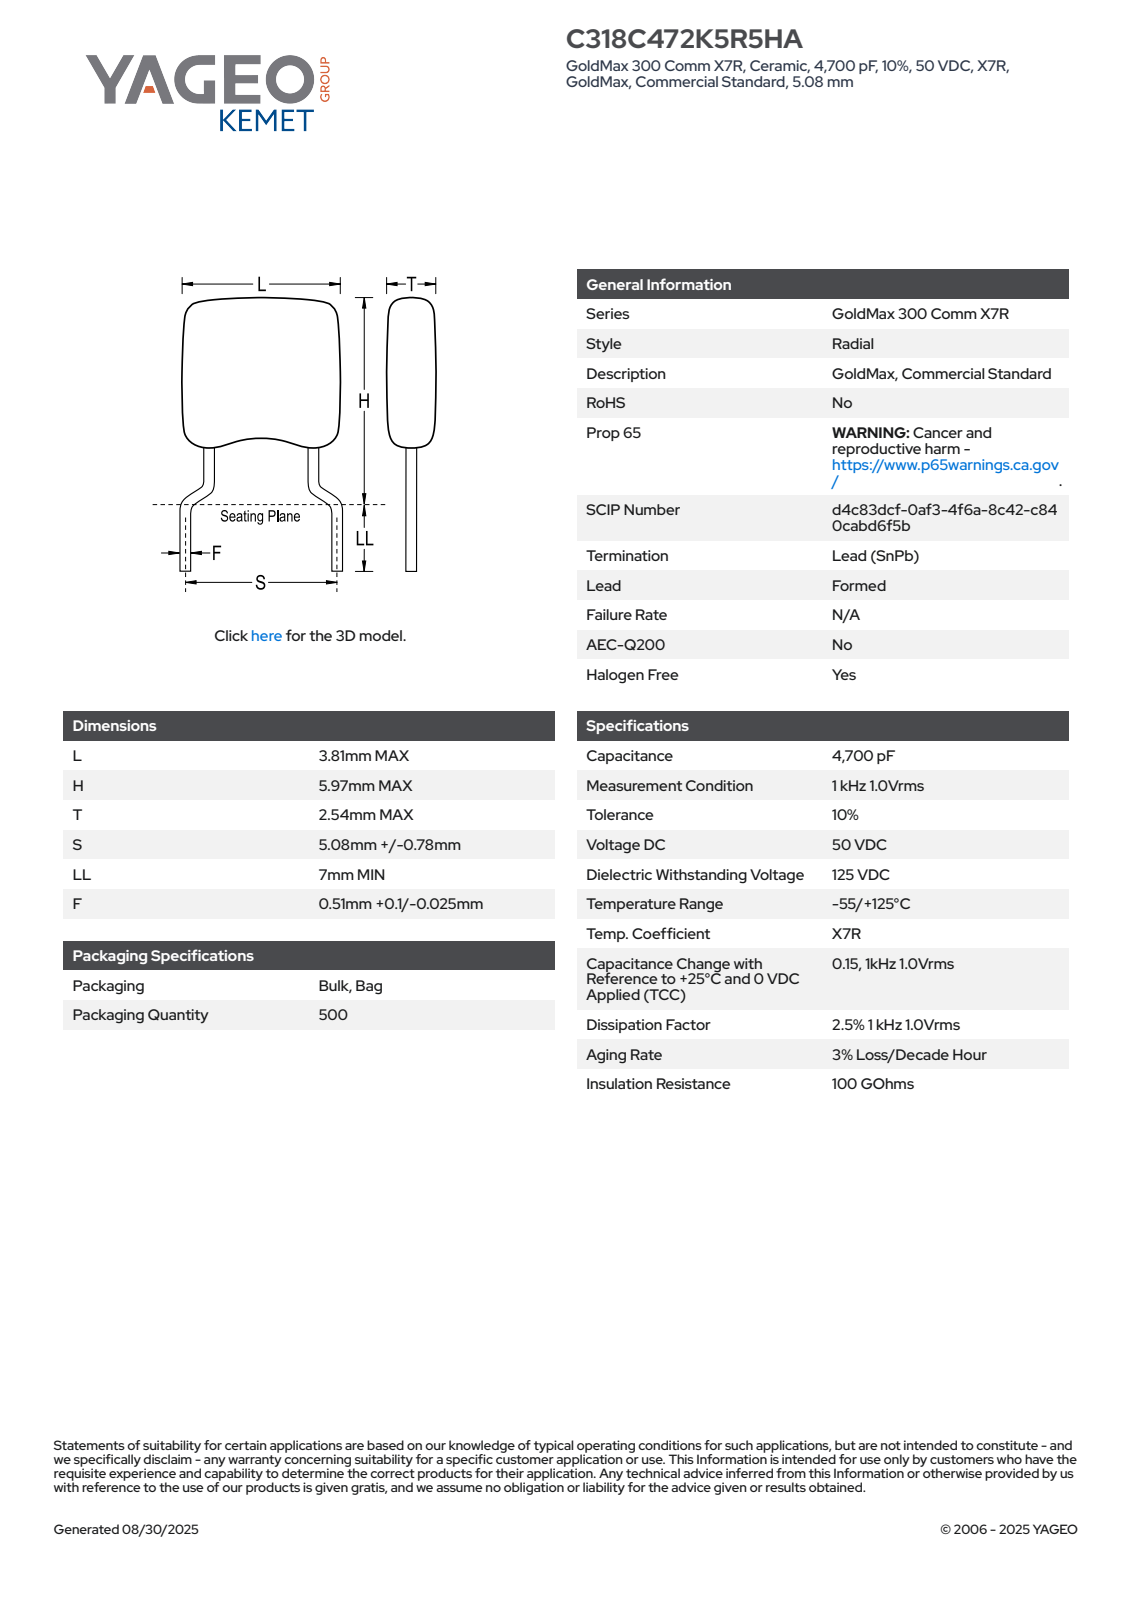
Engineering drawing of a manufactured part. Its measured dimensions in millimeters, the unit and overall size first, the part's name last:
Units: millimetres
Overall size (bounding box): 12.97 × 5.69 × 2.54
Round bosses / shafts (diameter × count): ⌀0.61 ×6
Partial cylindrical surfaces — rounded edges, fillets, slot ends (radius × count): R0.75 ×8, R1 ×2
Main face-to-face distances: 2.54, 3.81, 3.61, 9.36, 12.97, 0.32, 11.34, 1.98, 1.63, 11.02
Volume: 36 mm³ · Surface area: 91 mm²
Bodies: 4 solids, 109 faces (68 planar, 22 cylindrical, 19 other)
Part name (STEP PRODUCT): CCRC318_L3.81H5.97T2.54S5.08LL7F0.61
STEP written by: SolidWorks 2014 (AUTOMOTIVE_DESIGN)
